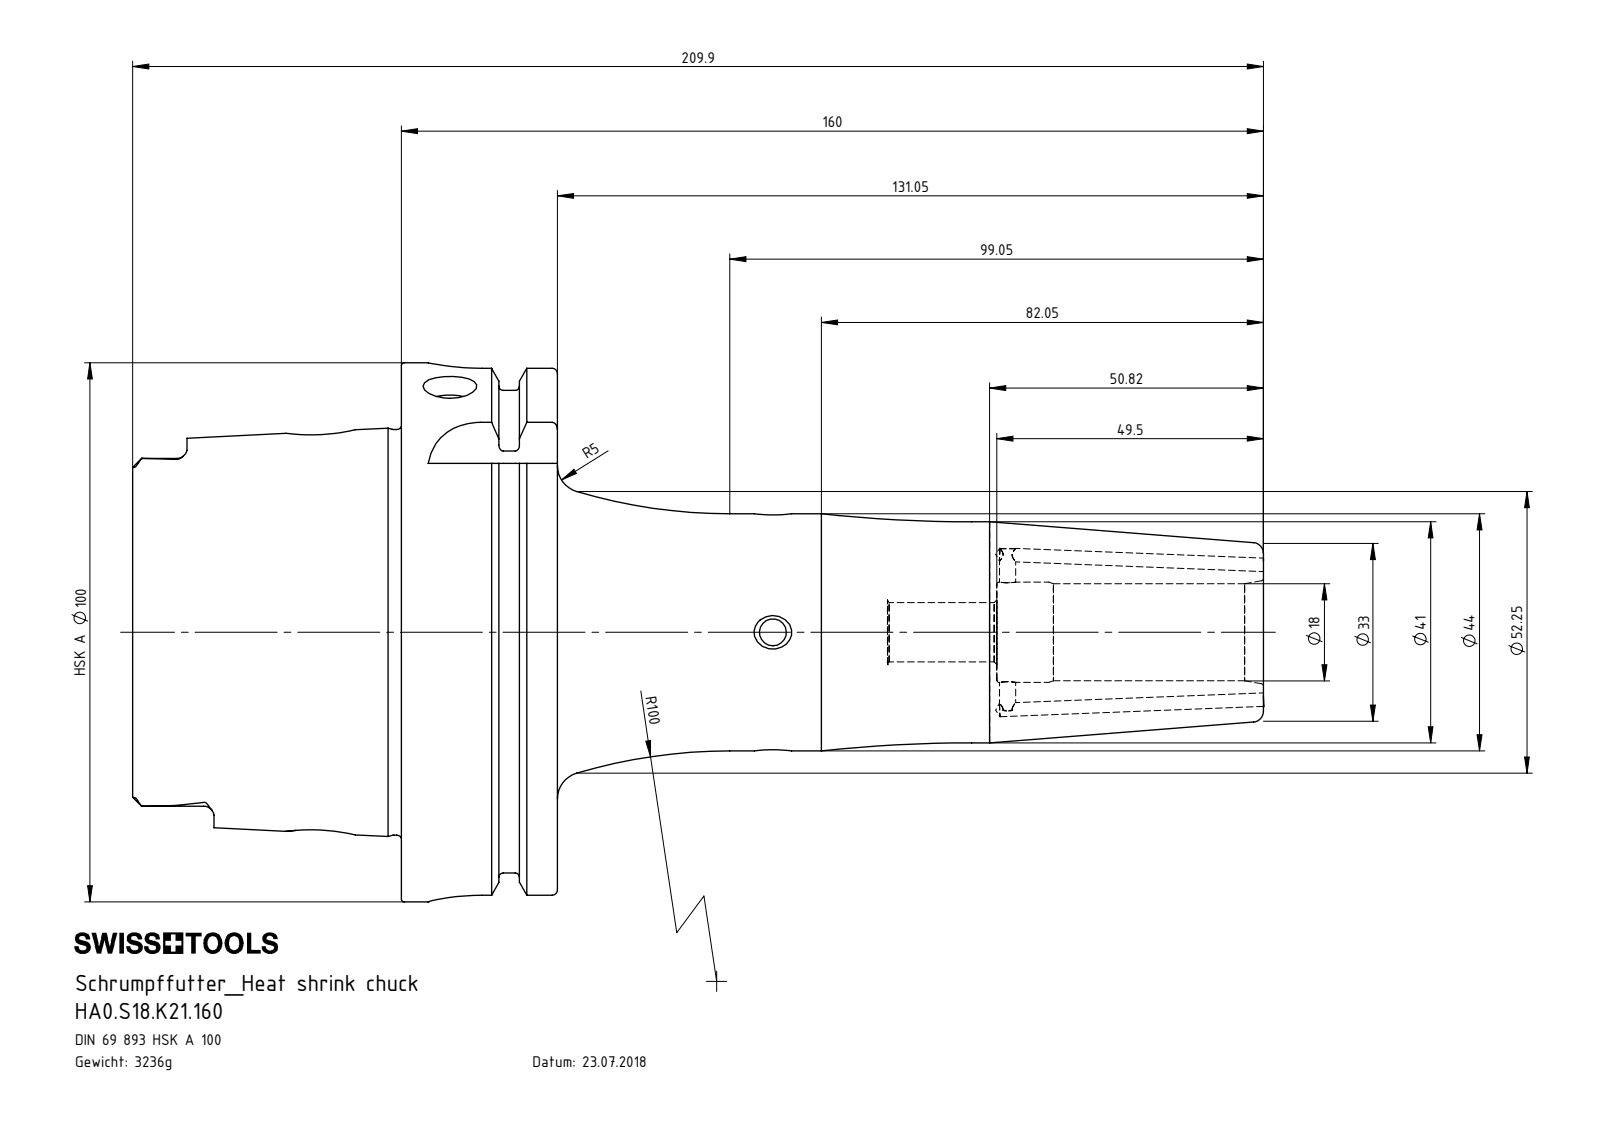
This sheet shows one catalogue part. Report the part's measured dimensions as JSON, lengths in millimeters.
{"part_name": "HA0-S18.K21.160_C_Fertigbearbeitung; ERU-AN5.K01.020_A; HA0.S18.K21.160; ERU-CJ2.001.006", "step_written_by": "SolidWorks 2017 (CONFIG_CONTROL_DESIGN)", "units": "millimeters", "bodies": {"solids": 4, "faces": 307, "planar": 95, "cylindrical": 89, "other": 123}, "overall_size": [209.98, 100, 100], "volume_mm3": 412191, "surface_area_mm2": 74030, "round_holes": [[10, 3], [2.5, 2], [5, 2], [12, 2], [3, 1], [6, 1], [11, 1], [18, 1], [18.6, 1], [22.5, 1], [26, 1], [53, 1]], "round_bosses_or_shafts": [[3, 2], [100, 1], [91.95, 1], [75.26, 1], [44, 1], [41, 1]], "partial_cylinders_radius": [[1.9, 6], [4.88, 4], [10, 4]], "face_to_face_distances": [28.95, 12.45, 16.5, 49.9, 62.35, 78.85, 87.8, 15.85, 78.2, 28.3], "hole_center_spacings": [43.55, 61.95, 83.95, 127.5]}
